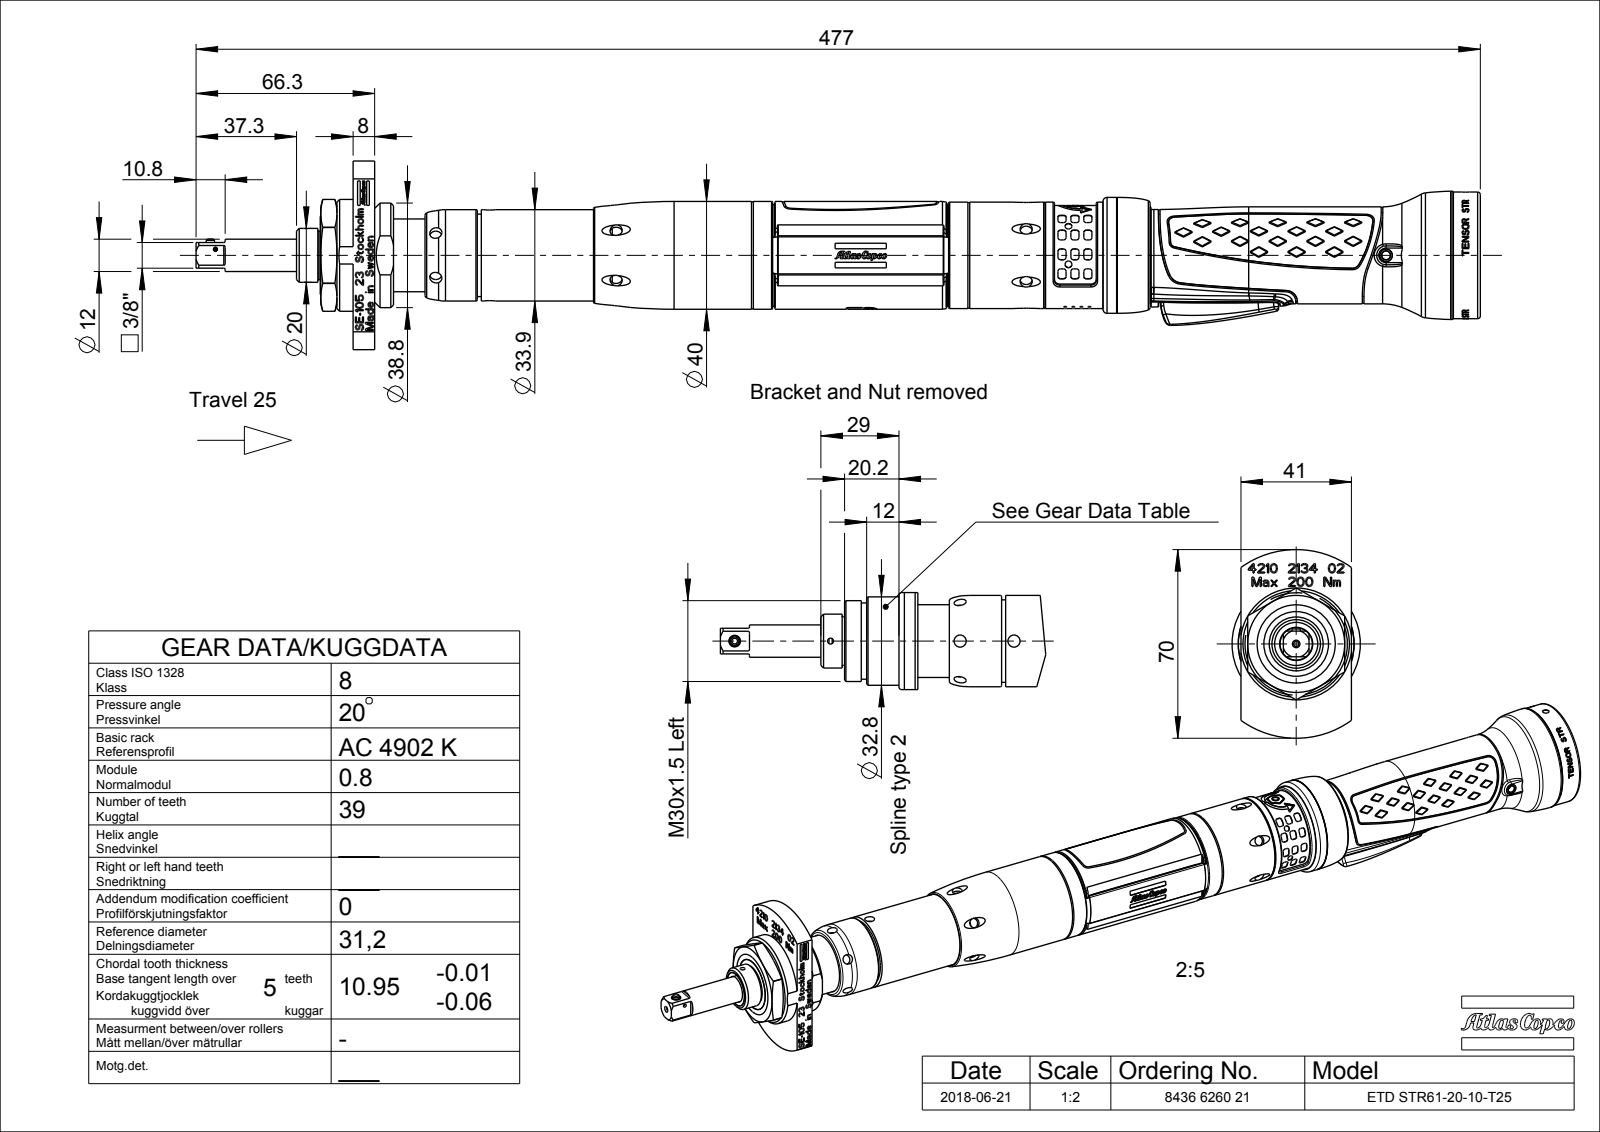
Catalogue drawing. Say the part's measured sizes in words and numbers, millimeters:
The part is named "4220502200; 4220435380-MONTERAD_ASM; 4220474480_ASM; 4220474580_ASM (+8 more)". Its 3-D file was written by "CREO PARAMETRIC BY PTC INC, 2016260 (CONFIG_CONTROL_DESIGN)". It is 38 solids with 8492 faces: 3264 planar, 1499 cylindrical and 3729 other. Overall it measures 476.78 by 49.81 by 47.62 millimeters. Its volume is 163 098 cubic millimeters and its surface area 166 090 square millimeters. Round holes: 12 of diameter 1, 12 of diameter 2.67, 12 of diameter 3.31, 10 of diameter 3.6, 10 of diameter 4.5, 8 of diameter 0.6, 4 of diameter 0.8, 4 of diameter 1.7, 4 of diameter 1.72, 4 of diameter 2.6, 2 of diameter 1.6, 2 of diameter 3.2. Round bosses or shafts: 8 of diameter 3.06, 8 of diameter 2.55, 8 of diameter 2.45, 8 of diameter 2.25, 8 of diameter 1.56, 4 of diameter 2.63, 4 of diameter 2.31, 4 of diameter 1.6. Partial cylindrical surfaces (rounded edges, fillets, slot ends): 149 of radius 0.2, 64 of radius 0.5, 47 of radius 0.3, 22 of radius 2, 16 of radius 1.12, 16 of radius 1.23, 12 of radius 3, 10 of radius 1.5. The main face-to-face distances are 0.87, 32.03, 32.9, 33.76, 31.16, 138.6, 380.48, 241.88, 2.5, 23. The hole center spacings are 3, 6, 4.48, 7.75, 15, 21.21, 4.4, 4.5.
